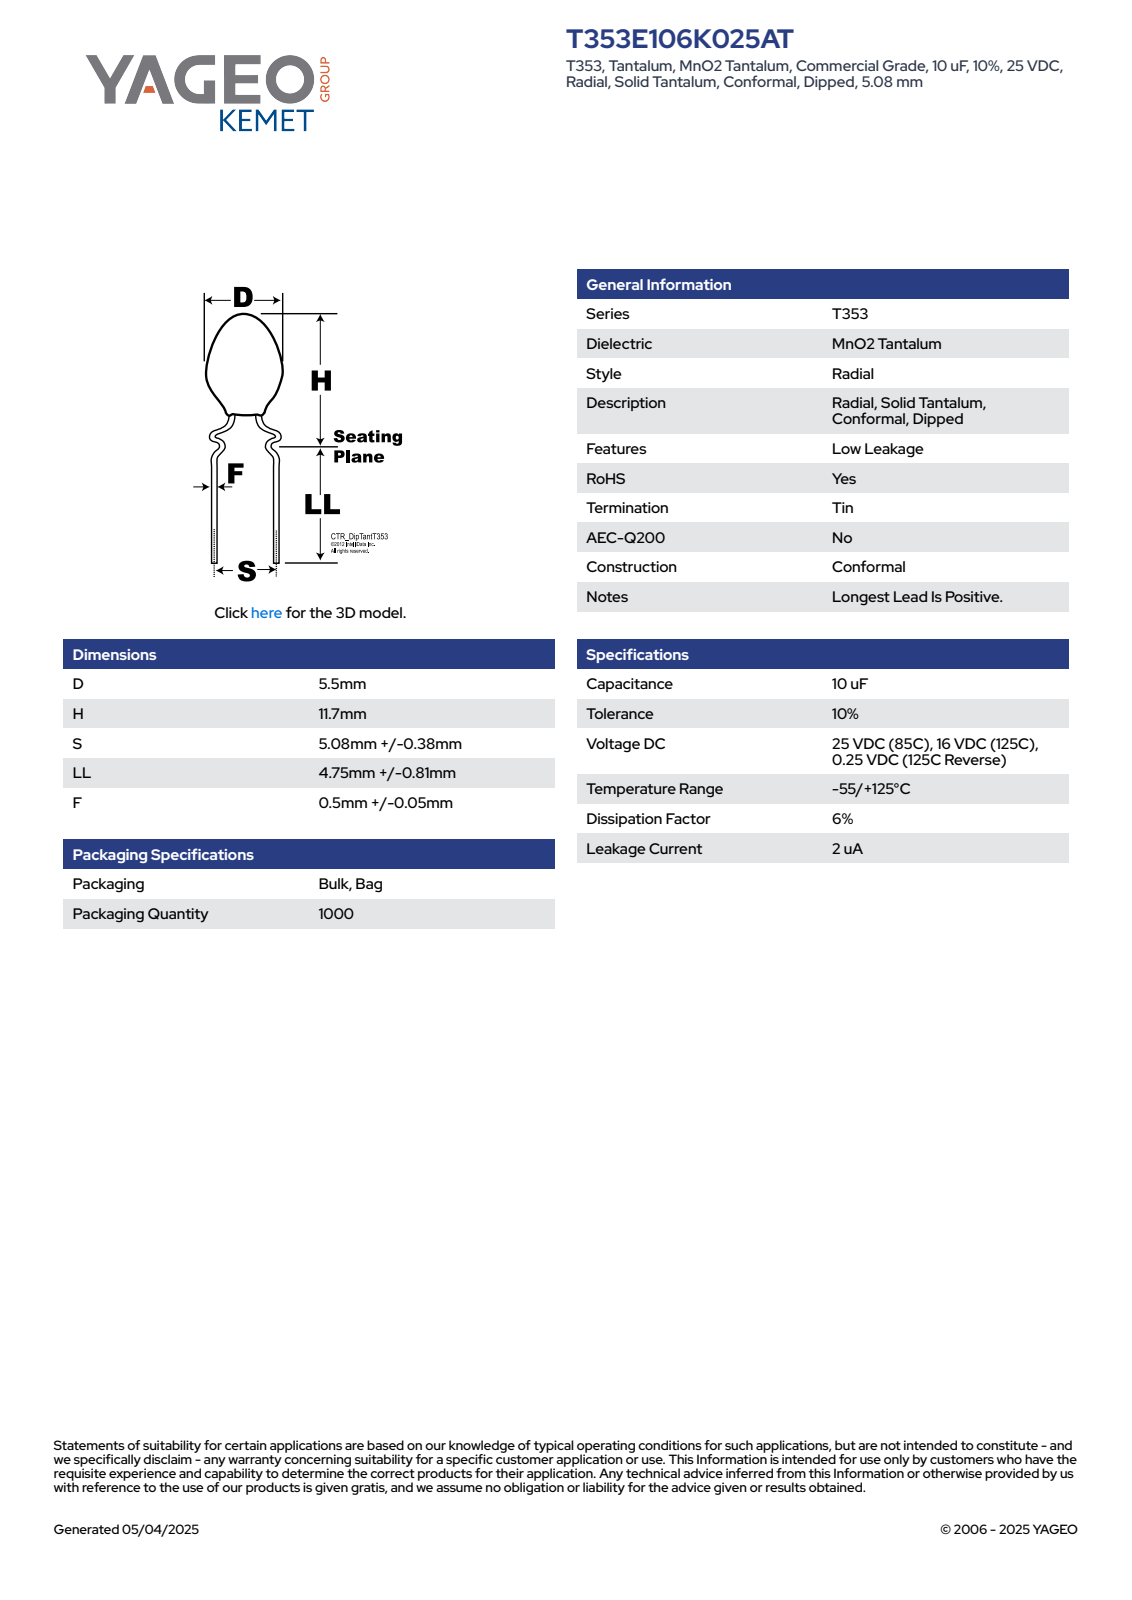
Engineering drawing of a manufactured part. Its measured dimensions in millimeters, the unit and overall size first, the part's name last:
Units: millimetres
Overall size (bounding box): 17.26 × 5.63 × 5.5
Round bosses / shafts (diameter × count): ⌀0.55 ×2, ⌀5.5 ×1
Partial cylindrical surfaces — rounded edges, fillets, slot ends (radius × count): R2.74 ×1
Main face-to-face distances: 8.03, 9.23, 17.26, 3.69, 4.34, 13.73, 4.5, 3.53, 12.92, 0.81
Volume: 172 mm³ · Surface area: 192 mm²
Bodies: 1 solid, 89 faces (29 planar, 10 cylindrical, 50 other)
Part name (STEP PRODUCT): CTR_T353_D5.5H11.7S5.08LL5.56F0.55
STEP written by: SolidWorks 2014 (AUTOMOTIVE_DESIGN)
